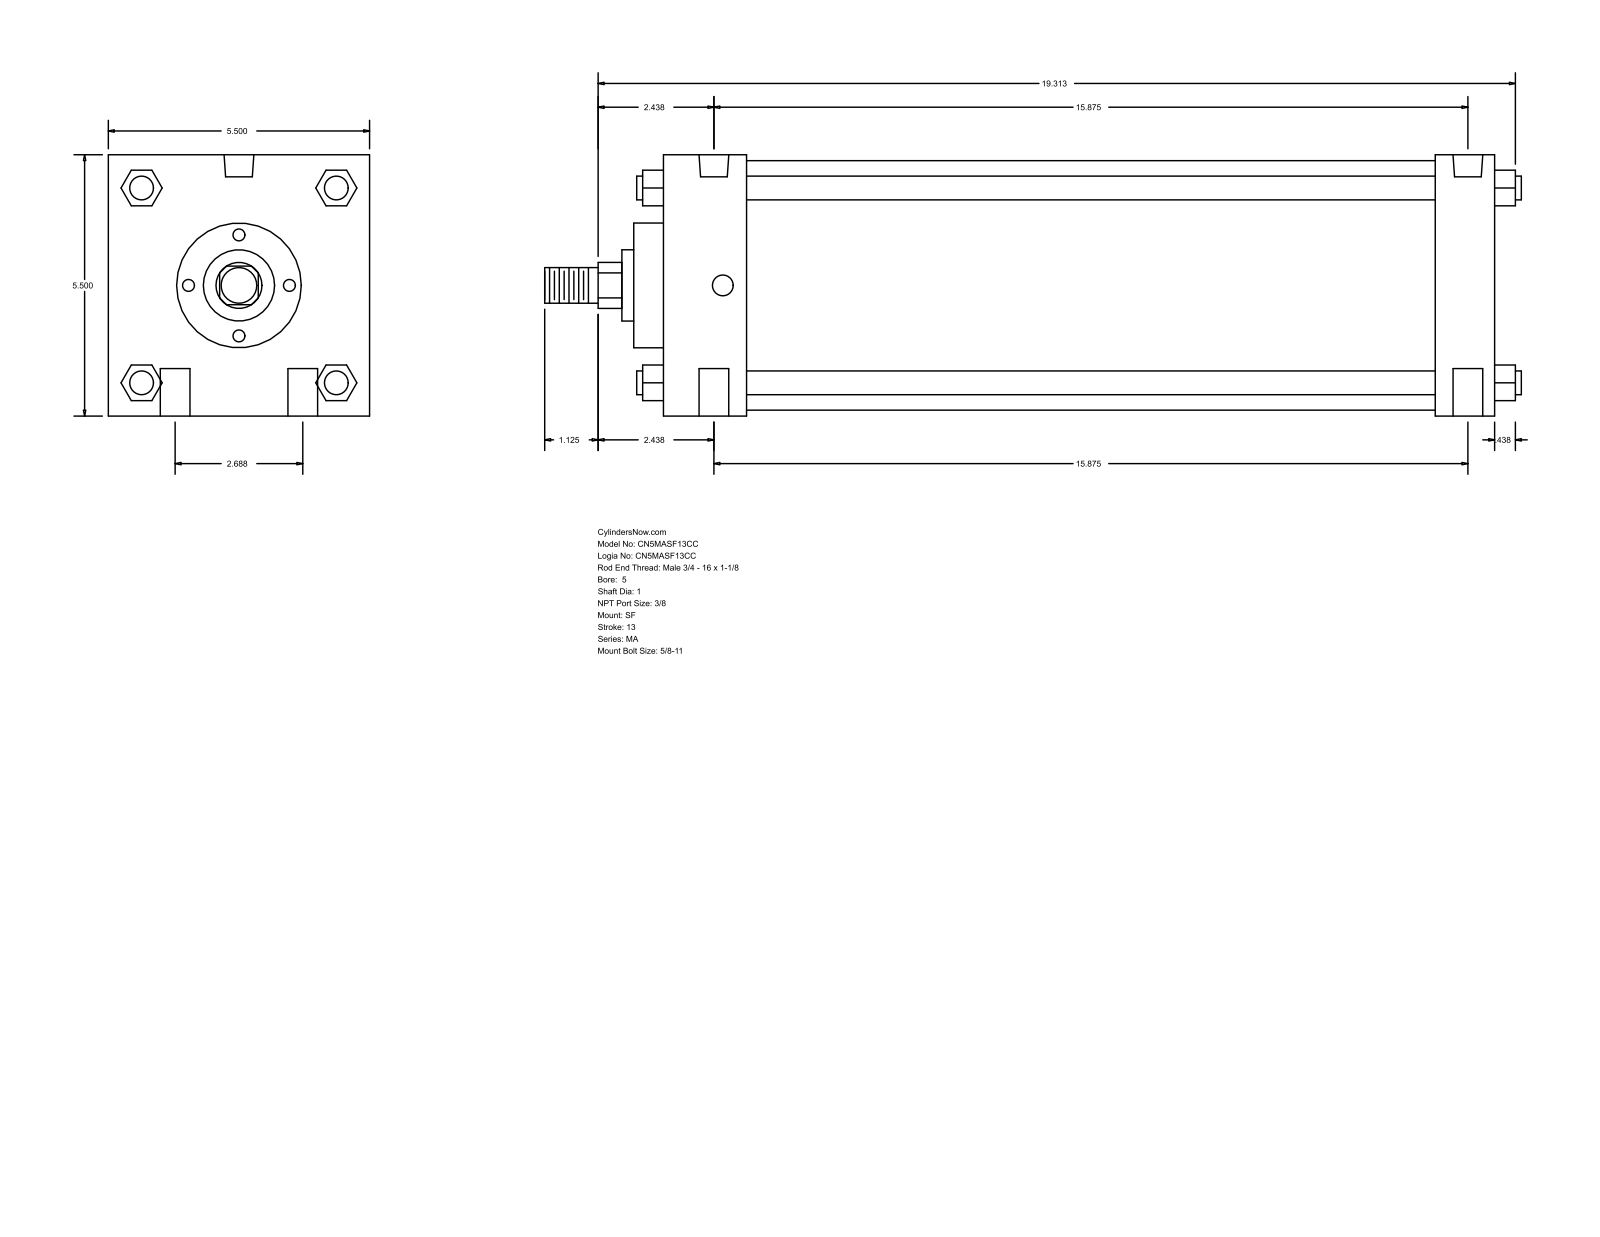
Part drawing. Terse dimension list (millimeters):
name: MA_SF__0500_1
written by: GSSL Pune (CONFIG_CONTROL_DESIGN)
unit: mm
bodies: 0 solids, 126 faces (95 planar, 31 cylindrical, 0 other)
size: 522.29 × 139.7 × 139.7
holes: 4× ⌀15.88, 2× ⌀11.11, 2× ⌀15.93
bosses: 4× ⌀12.7, 1× ⌀133.35, 1× ⌀66.67, 1× ⌀38.1, 1× ⌀25.4, 1× ⌀19.05
rounds: 1× R12.29
face distances: 139.7, 444.51, 44.46, 412.76, 368.3, 400.05, 31.75, 15.87, 60.33, 428.63
hole spacings: 34.13, 404.67, 403.23, 68.26, 408.97, 393.71
